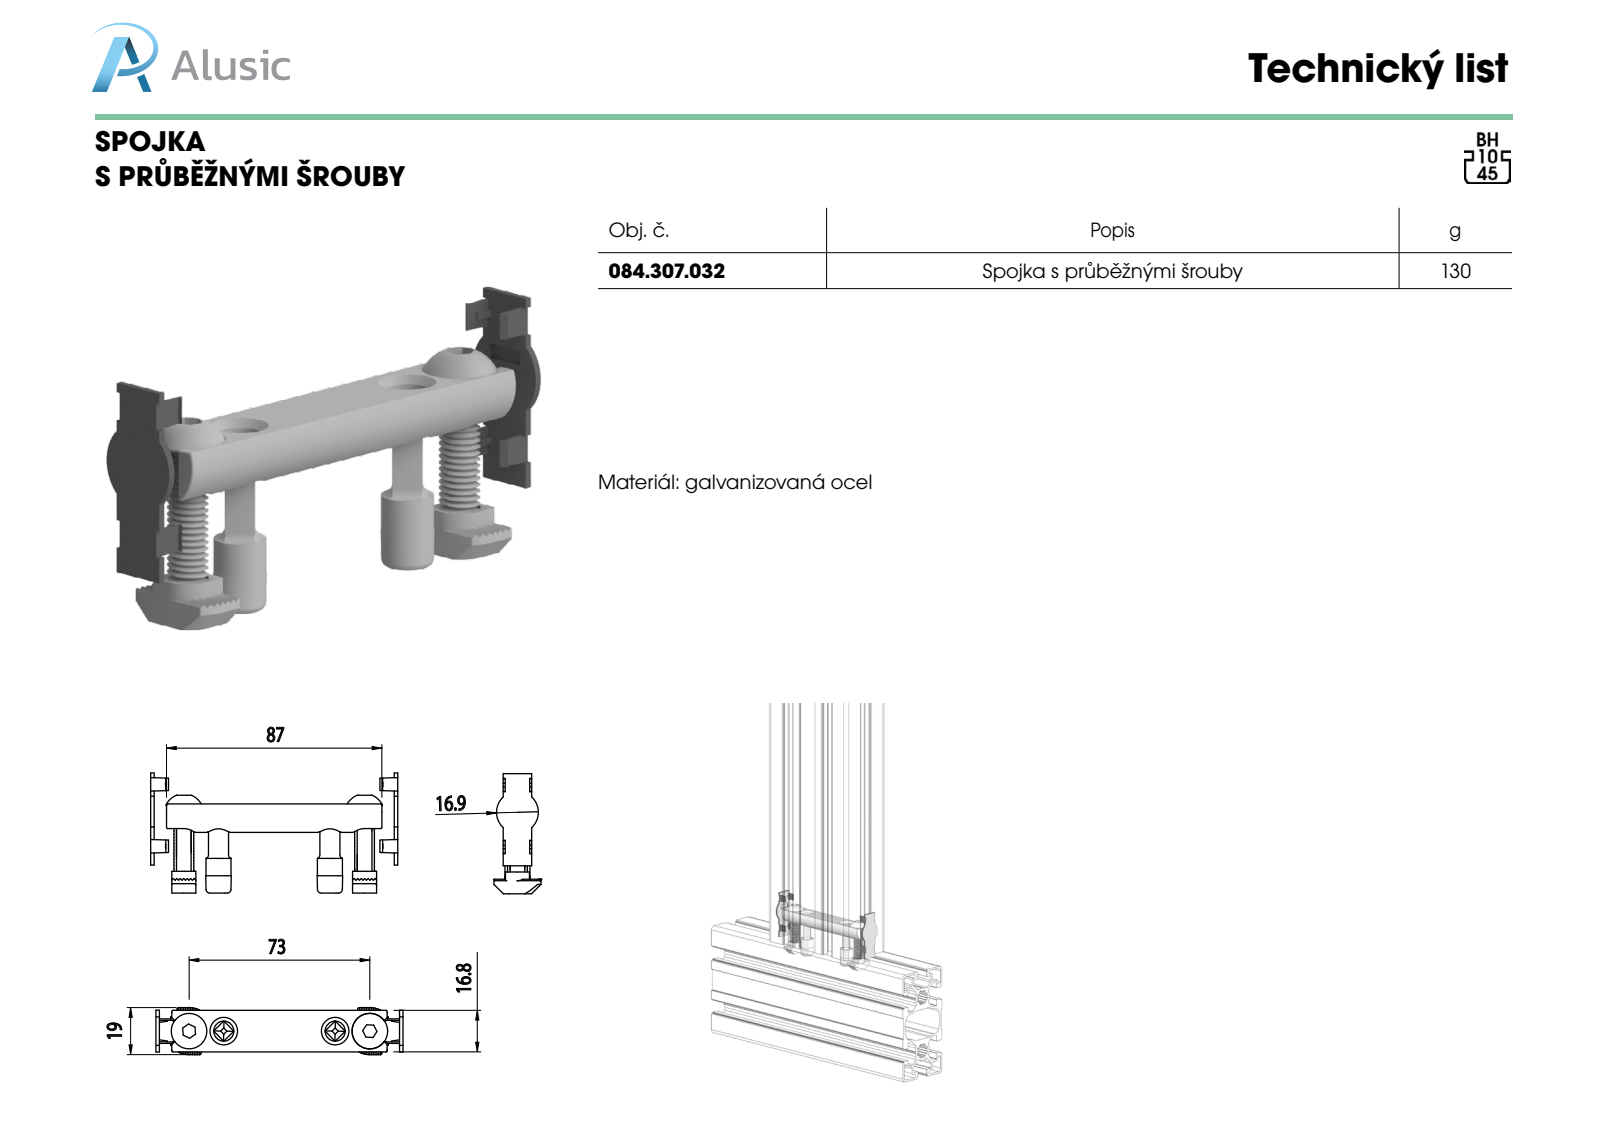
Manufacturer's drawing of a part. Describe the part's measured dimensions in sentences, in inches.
The part is named "084.307.032". Its 3-D file was written by "SolidWorks 2011 (CONFIG_CONTROL_DESIGN)". It is 9 solids with 606 faces: 311 planar, 181 cylindrical and 114 other. Overall it measures 3.929 by 1.909 by 0.748 inches. Its volume is 1.283 cubic inches and its surface area 23.08 square inches. Round holes: 2 of diameter 0.26, 2 of diameter 0.319. Round bosses or shafts: 2 of diameter 0.398, 2 of diameter 0.315. Partial cylindrical surfaces (rounded edges, fillets, slot ends): 24 of radius 0.02, 8 of radius 0.004, 8 of radius 0.059, 8 of radius 0.079, 6 of radius 0.012, 4 of radius 0.197, 2 of radius 0.165, 2 of radius 0.281. The main face-to-face distances are 0.055, 3.874, 3.929, 3.819, 0.039, 0.228, 1.378, 1.417, 0.039, 0.36. The hole center spacings are 0.551, 2.323, 1.772, 2.874.
